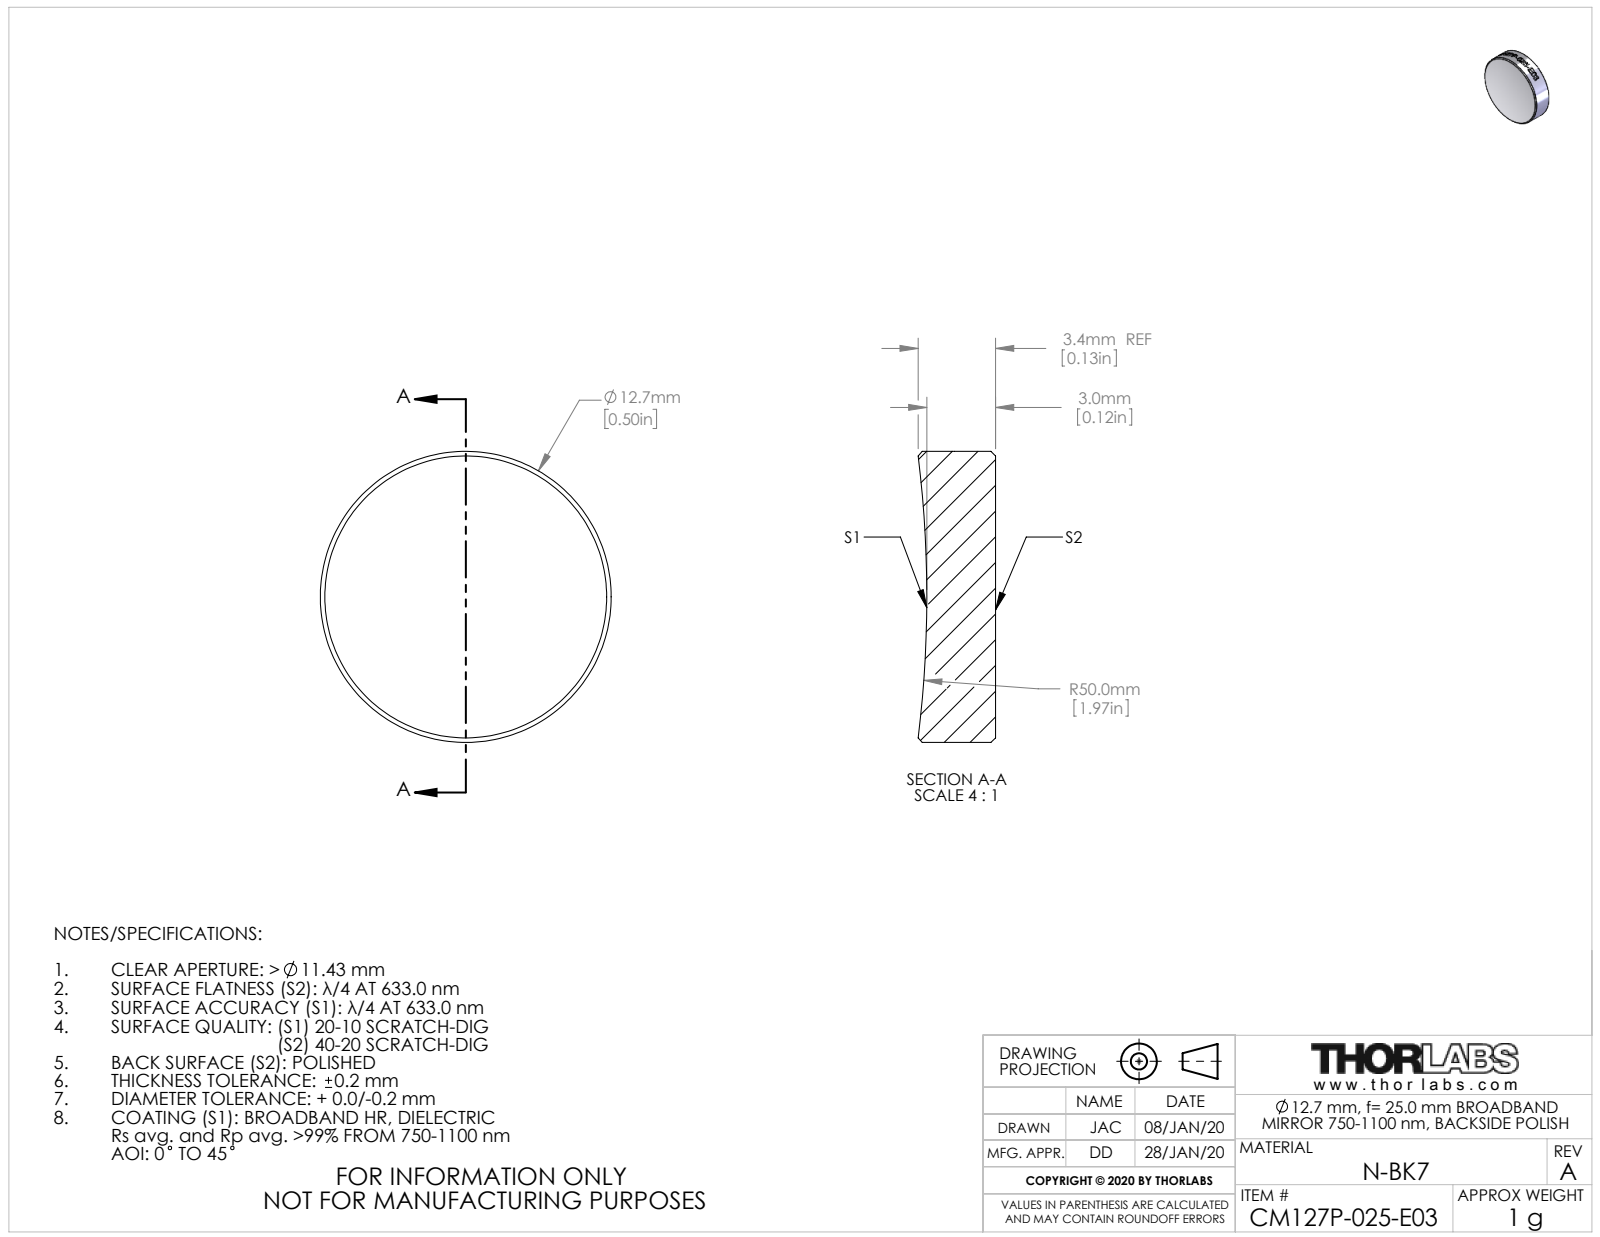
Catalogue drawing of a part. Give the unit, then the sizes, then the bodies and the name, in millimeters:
Units: millimetres
Overall size (bounding box): 12.7 × 12.7 × 3.38
Round bosses / shafts (diameter × count): ⌀12.7 ×1
Volume: 404 mm³ · Surface area: 380 mm²
Bodies: 1 solid, 26 faces (1 planar, 19 cylindrical, 6 other)
Part name (STEP PRODUCT): TTN201382-E0W
STEP written by: SolidWorks 2018 (CONFIG_CONTROL_DESIGN)
